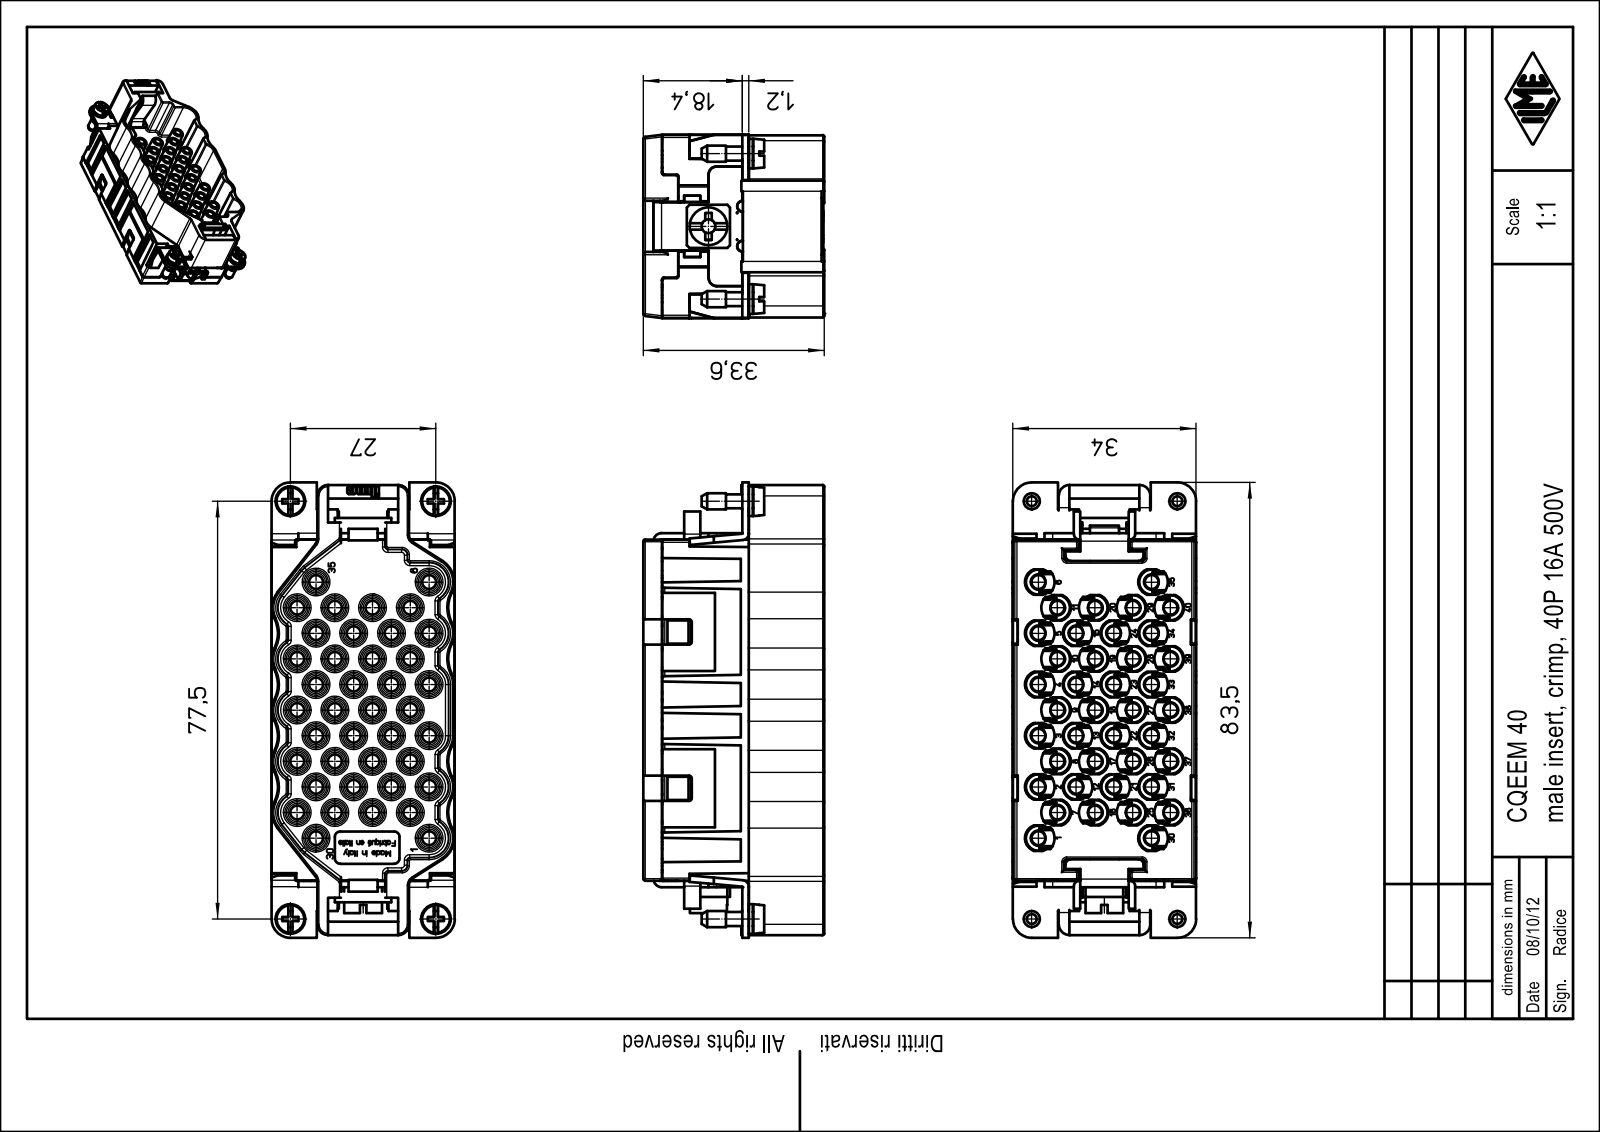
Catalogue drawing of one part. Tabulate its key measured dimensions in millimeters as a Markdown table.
| quantity | value |
| --- | --- |
| part name | CQEEM_40 |
| STEP written by | Creo Elements/Direct Modeling 18.0B 02-Dec-2011 (C) Parametric Technology GmbH (AUTOMOTIVE_DESIGN) |
| units | millimeters |
| bodies | 1 solid, 5660 faces (5135 planar, 347 cylindrical, 178 other) |
| overall size | 84.5 × 34 × 33.6 |
| volume | 32 971 mm³ |
| surface area | 35 707 mm² |
| round holes (diameter × count) | 2.6 × 40, 5 × 40, 2.8 × 4, 2.58 × 1, 3 × 1 |
| round bosses / shafts (diameter × count) | 5.5 × 4, 3 × 4, 2.6 × 4, 7 × 1, 6 × 1 |
| partial cylindrical surfaces (radius × count) | 3 × 40, 1 × 16, 3.55 × 11, 4.65 × 11, 6.16 × 8, 2 × 6, 0.29 × 5, 1.2 × 4 |
| main face-to-face distances | 1.2, 18.6, 33.1, 0.9, 15, 7.6, 34, 2.5, 8.9, 72.1 |
| hole center spacings | 5.9, 14.67, 11.8, 24.01, 9.5, 11.52, 18.13, 20.25 |
